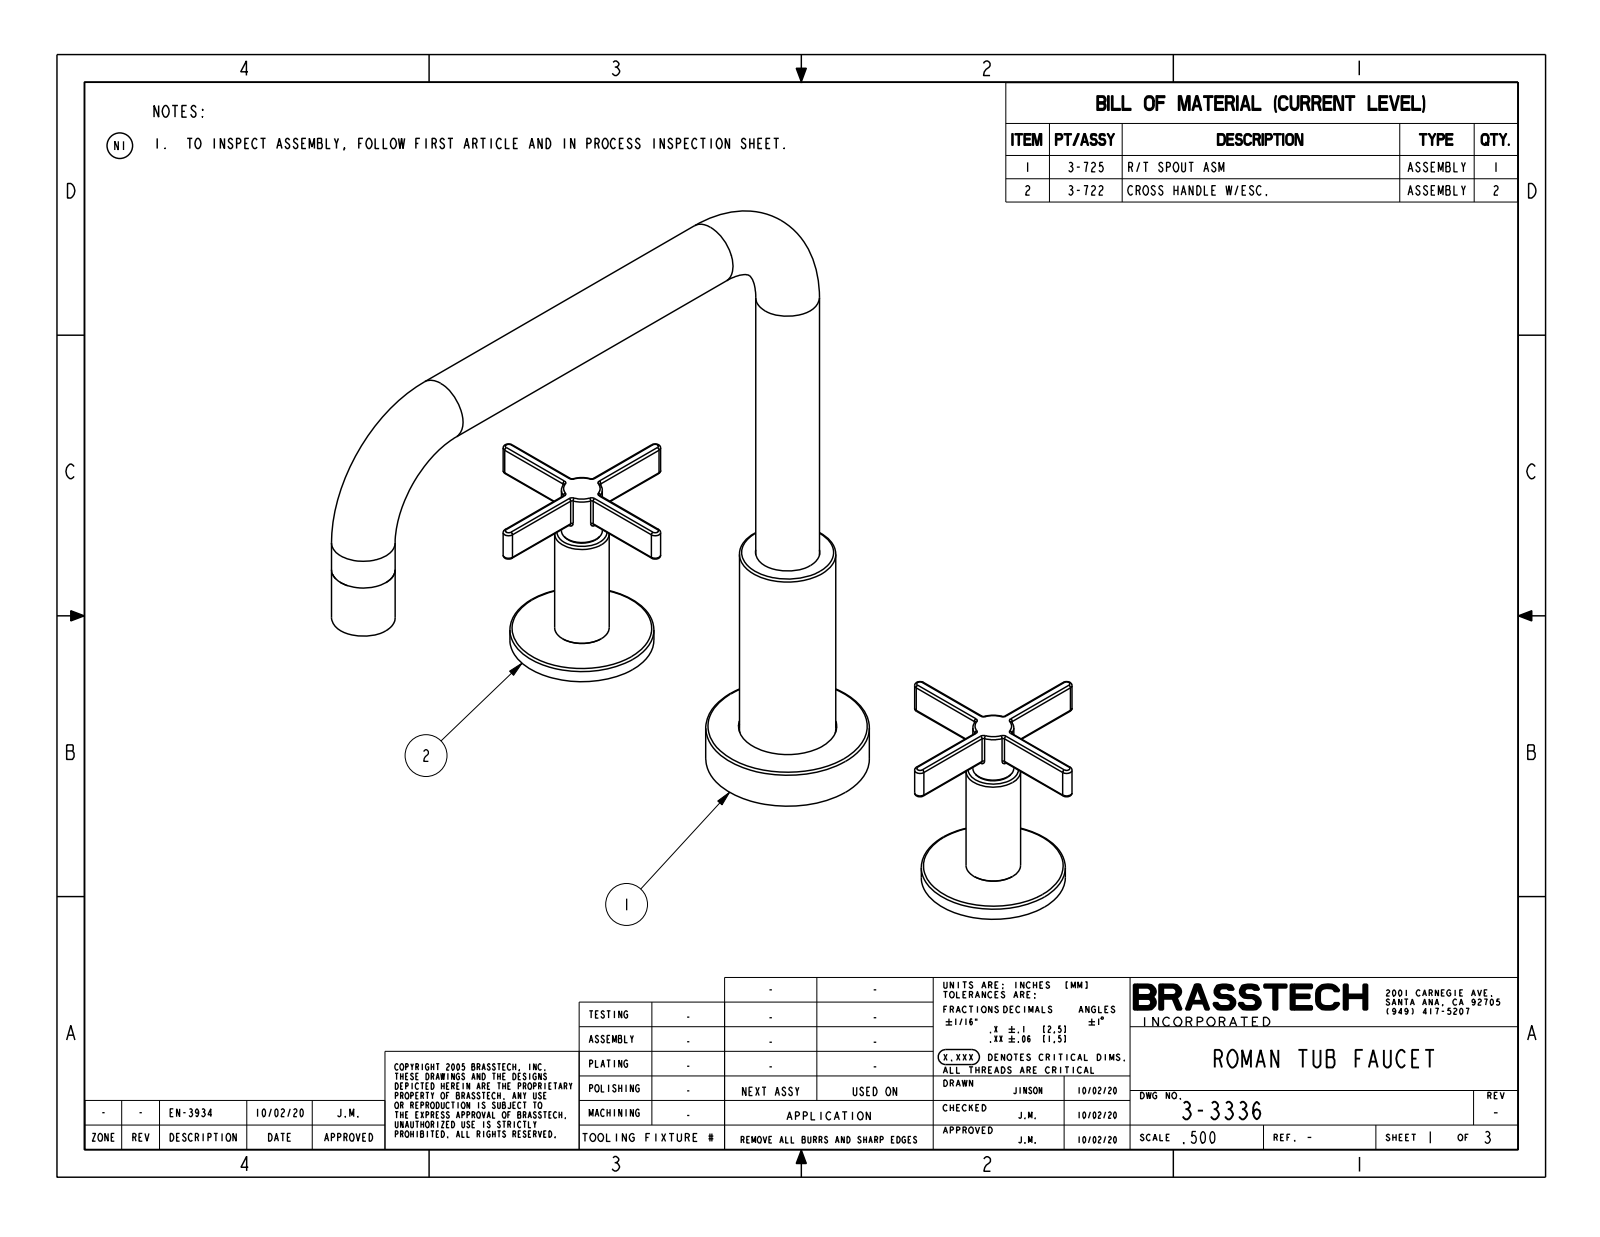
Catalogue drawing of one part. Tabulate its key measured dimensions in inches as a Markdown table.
| quantity | value |
| --- | --- |
| part name | 13539; 20-571_ASM; 13540; 13139 (+8 more) |
| STEP written by | CREO PARAMETRIC BY PTC INC, 2018400 (CONFIG_CONTROL_DESIGN) |
| units | inches |
| bodies | 11 solids, 673 faces (198 planar, 305 cylindrical, 170 other) |
| overall size | 11 × 10.187 × 9.748 |
| volume | 8.66 in³ |
| surface area | 171.3 in² |
| round holes (diameter × count) | 0.751 × 3, 0.11 × 2, 0.36 × 2, 0.397 × 2, 0.4 × 2, 0.516 × 2, 0.535 × 2, 0.6 × 2, 0.7 × 2, 1.6 × 2, 1.89 × 2, 0.118 × 1 |
| round bosses / shafts (diameter × count) | 0.875 × 3, 0.68 × 3, 2 × 2, 1.65 × 2, 0.75 × 2, 0.73 × 2, 0.563 × 2, 0.51 × 2 |
| partial cylindrical surfaces (radius × count) | 0.03 × 28, 0.075 × 8, 0.137 × 2, 0.3 × 1 |
| main face-to-face distances | 0.15, 0.05, 0.375, 0.325, 0.15, 0.12, 0.07, 0.445, 0.2, 0.08 |
| hole center spacings | 4, 9.169, 8, 8.25 |
